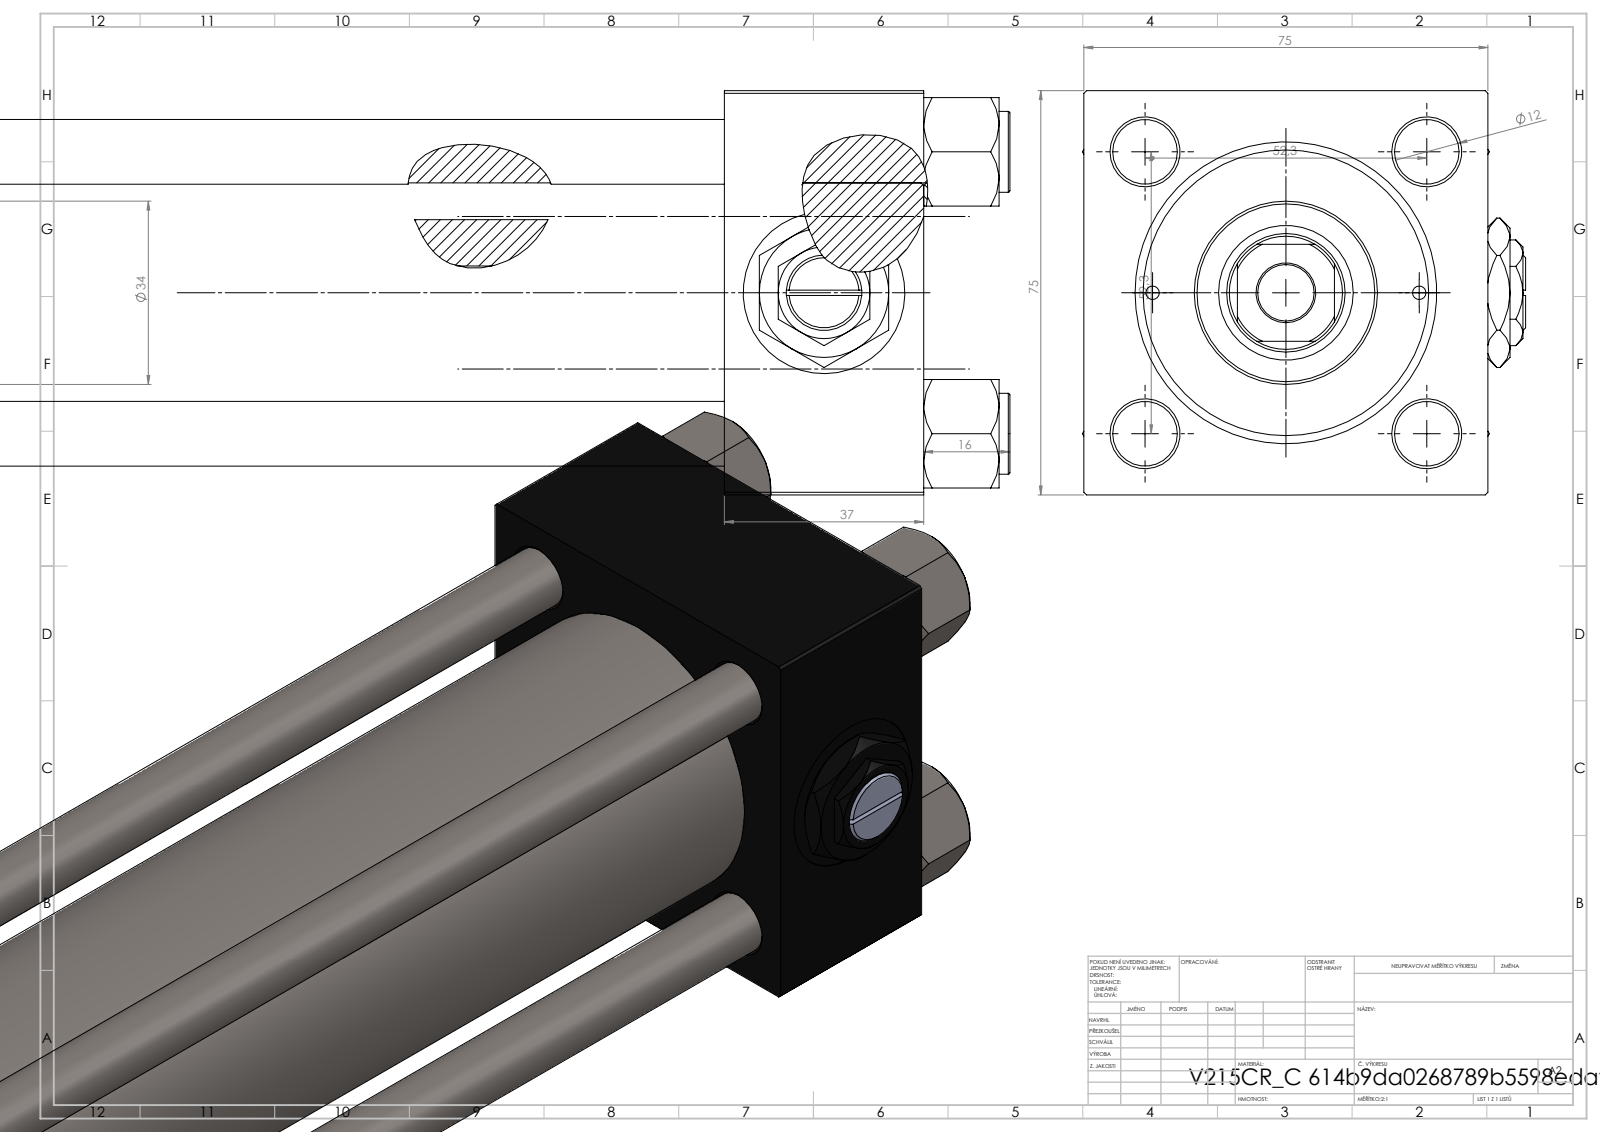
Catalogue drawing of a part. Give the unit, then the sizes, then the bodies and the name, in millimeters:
Units: millimetres
Overall size (bounding box): 475 × 82.27 × 75
Round holes (diameter × count): ⌀12 ×4, ⌀2.5 ×2, ⌀7 ×2, ⌀20.96 ×2, ⌀30 ×2, ⌀10.5 ×1, ⌀22 ×1, ⌀25 ×1, ⌀41 ×1, ⌀50 ×1, ⌀53 ×1
Round bosses / shafts (diameter × count): ⌀15 ×4, ⌀56 ×1, ⌀34 ×1
Partial cylindrical surfaces — rounded edges, fillets, slot ends (radius × count): R10.5 ×1
Main face-to-face distances: 75, 37, 434, 397, 375, 338, 59, 405.3, 368.3, 30.3
Hole centre spacings: 26.19, 36.98, 52.3, 57.22, 24.75, 73.96, 49.5, 373.5
Volume: 1 025 000 mm³ · Surface area: 306 659 mm²
Bodies: 13 solids, 1255 faces (575 planar, 102 cylindrical, 578 other)
Part name (STEP PRODUCT): V215CR_VCP_C; V215CR_C_TYCINKA; V215_VC_A; Zatka_pro_OIL_PORT (+2 more)
STEP written by: SolidWorks 2019 (CONFIG_CONTROL_DESIGN)
